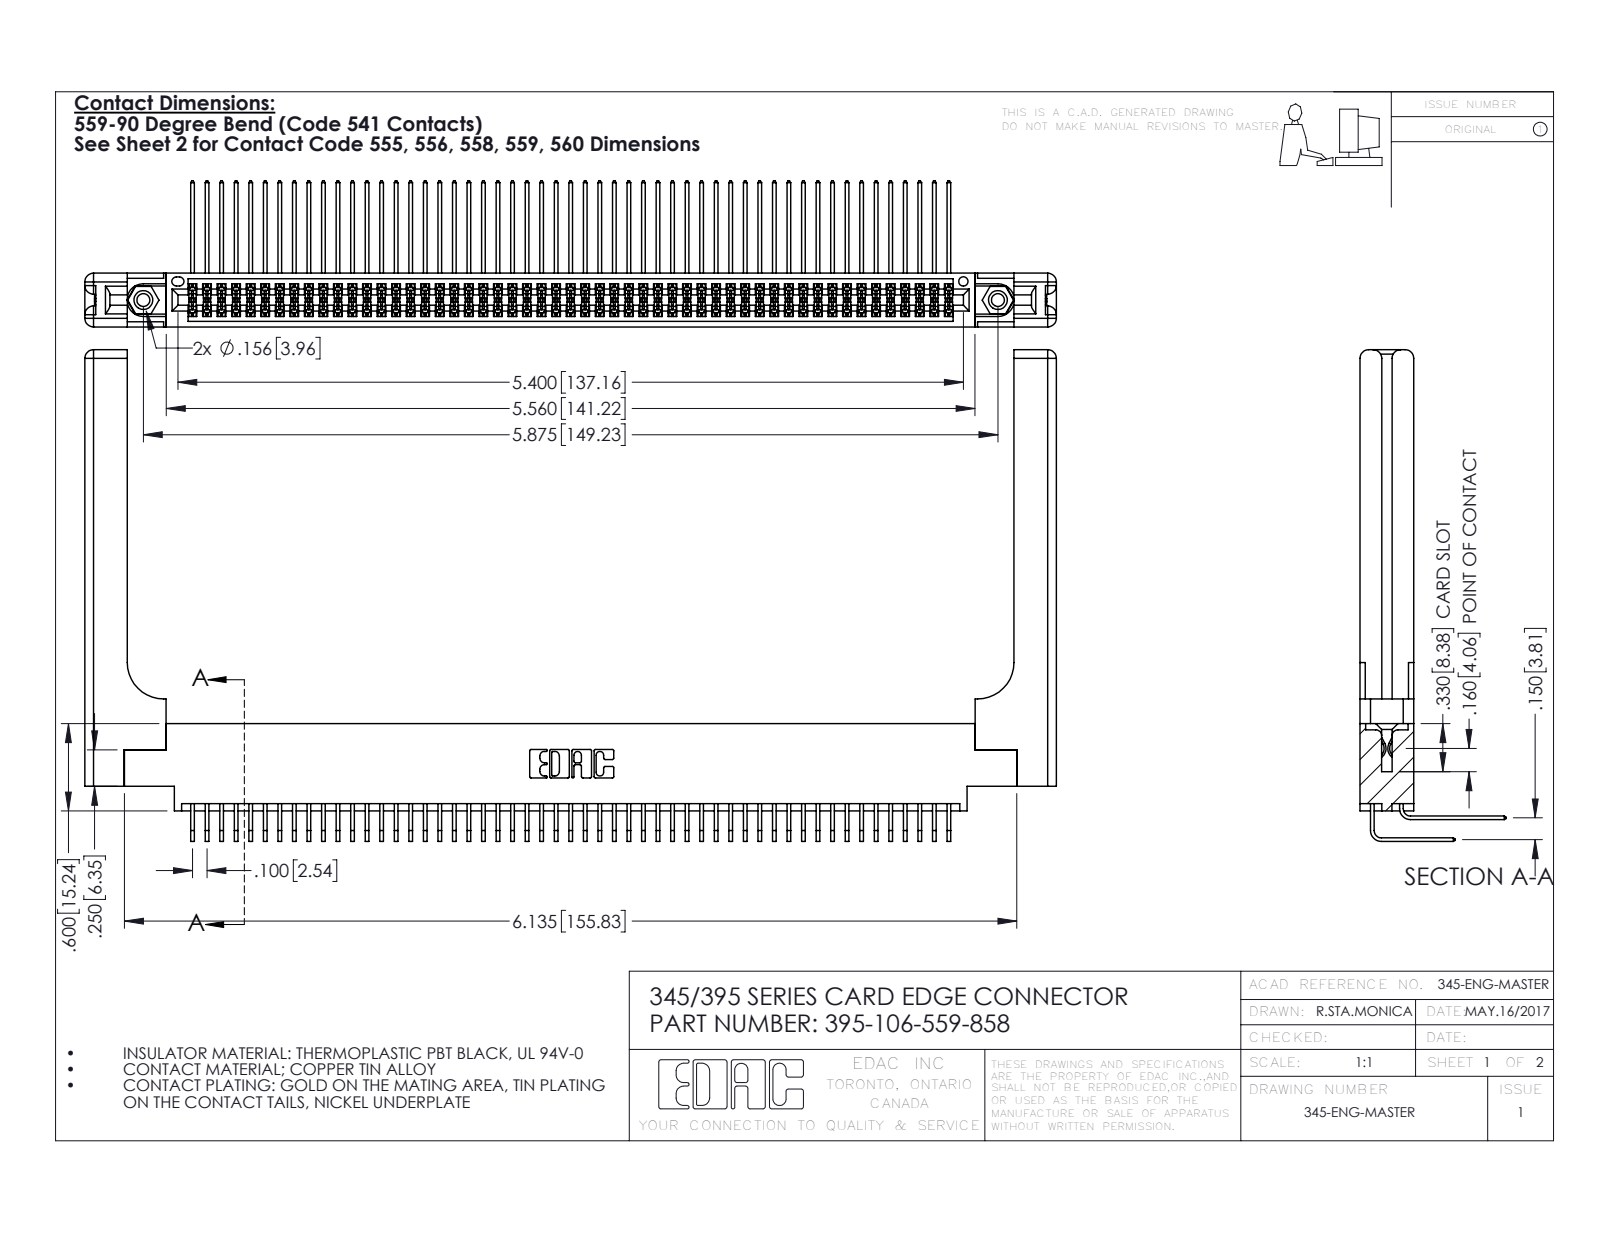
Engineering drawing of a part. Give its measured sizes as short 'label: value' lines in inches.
name: 345-220-058_345-220-058; 345 Part_0.170 Offset - 0.156 Dia-TH; 395-106-559-858; 345-292-001_558 559 Tail - 1 (+2 more)
written by: SolidWorks 2016 (CONFIG_CONTROL_DESIGN)
unit: in
bodies: 111 solids, 5898 faces (3942 planar, 1896 cylindrical, 60 other)
size: 6.679 × 3.379 × 1.005
volume: 1.559 in³; area: 51.98 in²
holes: 2× ⌀0.089, 2× ⌀0.125, 2× ⌀0.156, 1× ⌀0.064
bosses: 2× ⌀0.155
rounds: 159× R0.006, 22× R0.01, 16× R0.06, 6× R0.007, 6× R0.031, 3× R0.026, 2× R0.014, 2× R0.019
face distances: 0.072, 0.298, 0.37, 0.098, 0.272, 0.025, 0.2, 0.225, 0.175, 0.15
hole spacings: 0.27, 5.639, 5.875
